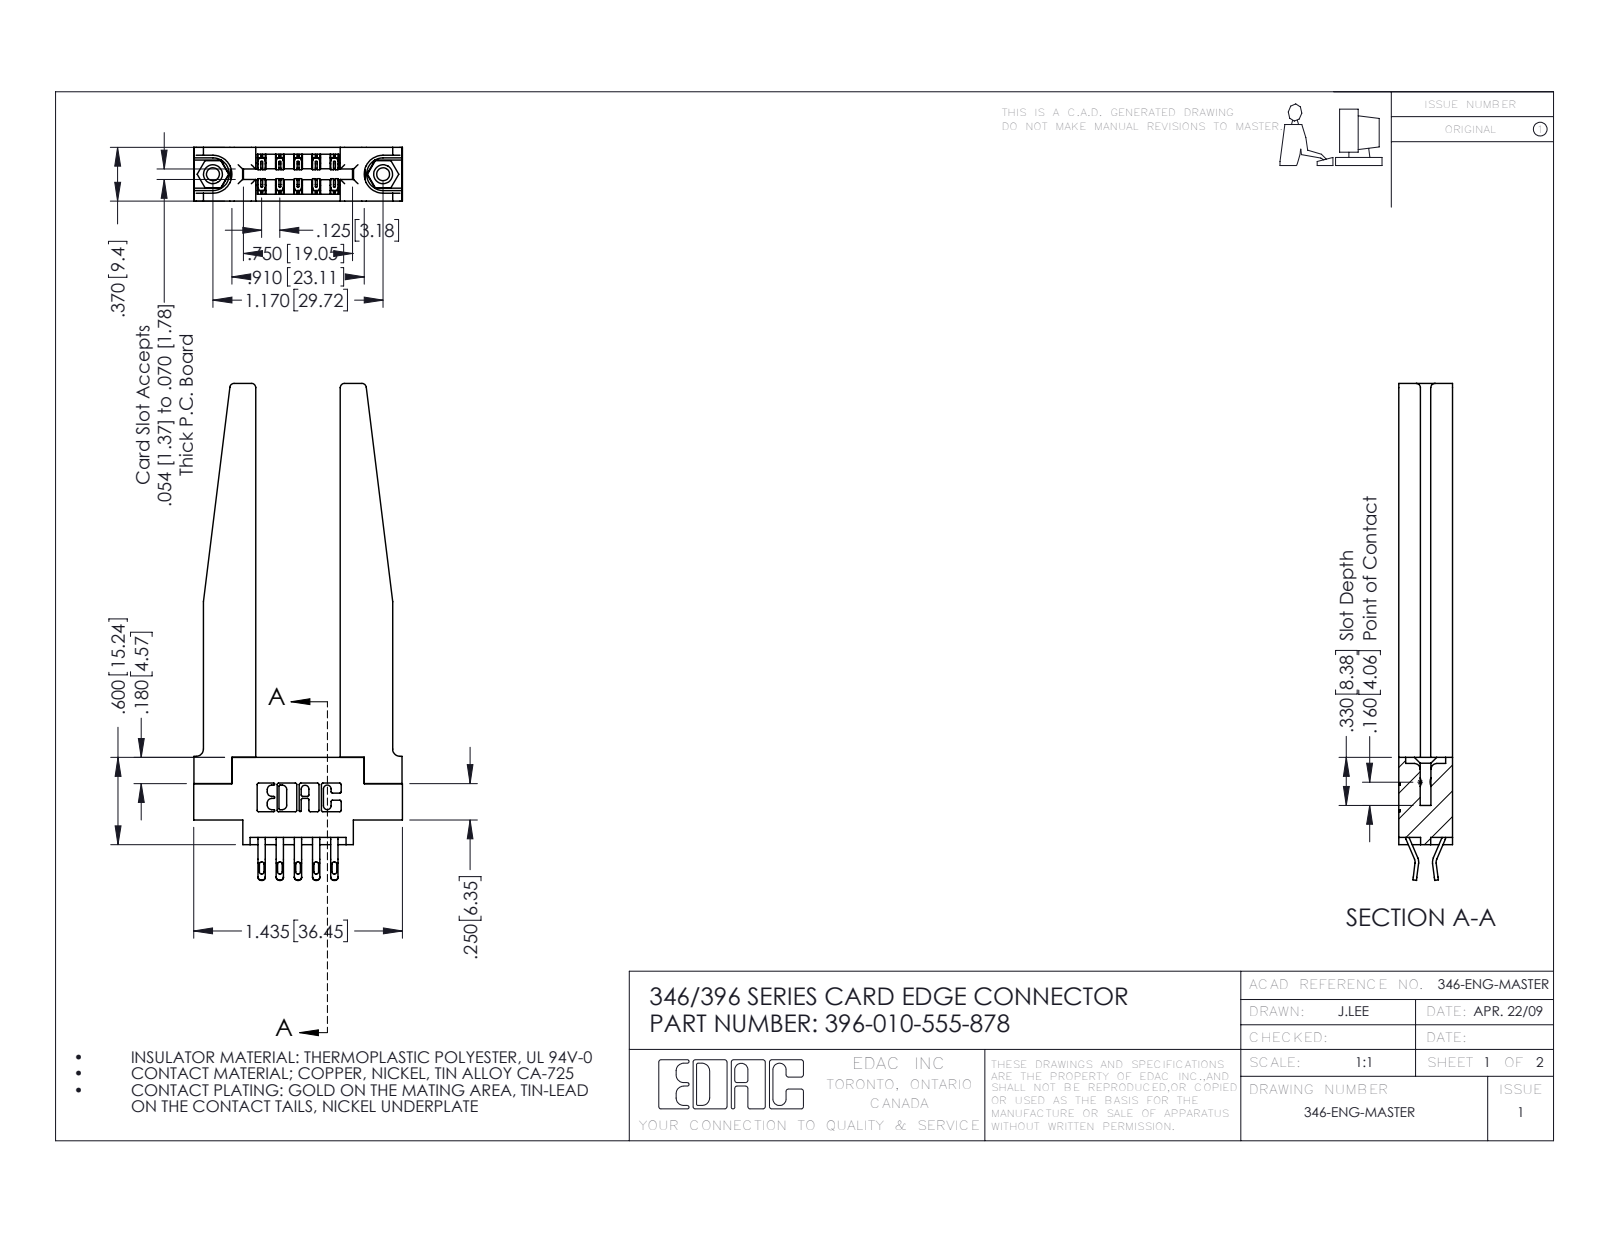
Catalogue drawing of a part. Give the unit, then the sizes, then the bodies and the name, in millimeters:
Units: millimetres
Overall size (bounding box): 86.7 × 36.4 × 9.4
Round holes (diameter × count): ⌀2.3 ×2, ⌀3.2 ×2, ⌀4 ×2, ⌀1.6 ×1
Round bosses / shafts (diameter × count): ⌀3.9 ×2
Partial cylindrical surfaces — rounded edges, fillets, slot ends (radius × count): R0.3 ×22, R0.4 ×20, R0.5 ×20, R0.2 ×15, R0.8 ×8, R0.2 ×6, R0.8 ×6, R1.3 ×4
Main face-to-face distances: 9.4, 3.8, 5.6, 14.8, 6.4, 3.8, 1.8, 2.6, 1.2, 8.2
Hole centre spacings: 6.2, 24.6, 29.7
Volume: 10 000 mm³ · Surface area: 10 550 mm²
Bodies: 15 solids, 940 faces (552 planar, 336 cylindrical, 52 other)
Part name (STEP PRODUCT): 396-010-555-878; 346 Part_0.170 Offset - 0.156 Dia-TH; 345-292-001_555 Tail; 345-250-001_345-250-001-102 (+1 more)
STEP written by: SolidWorks 2016 (CONFIG_CONTROL_DESIGN)
